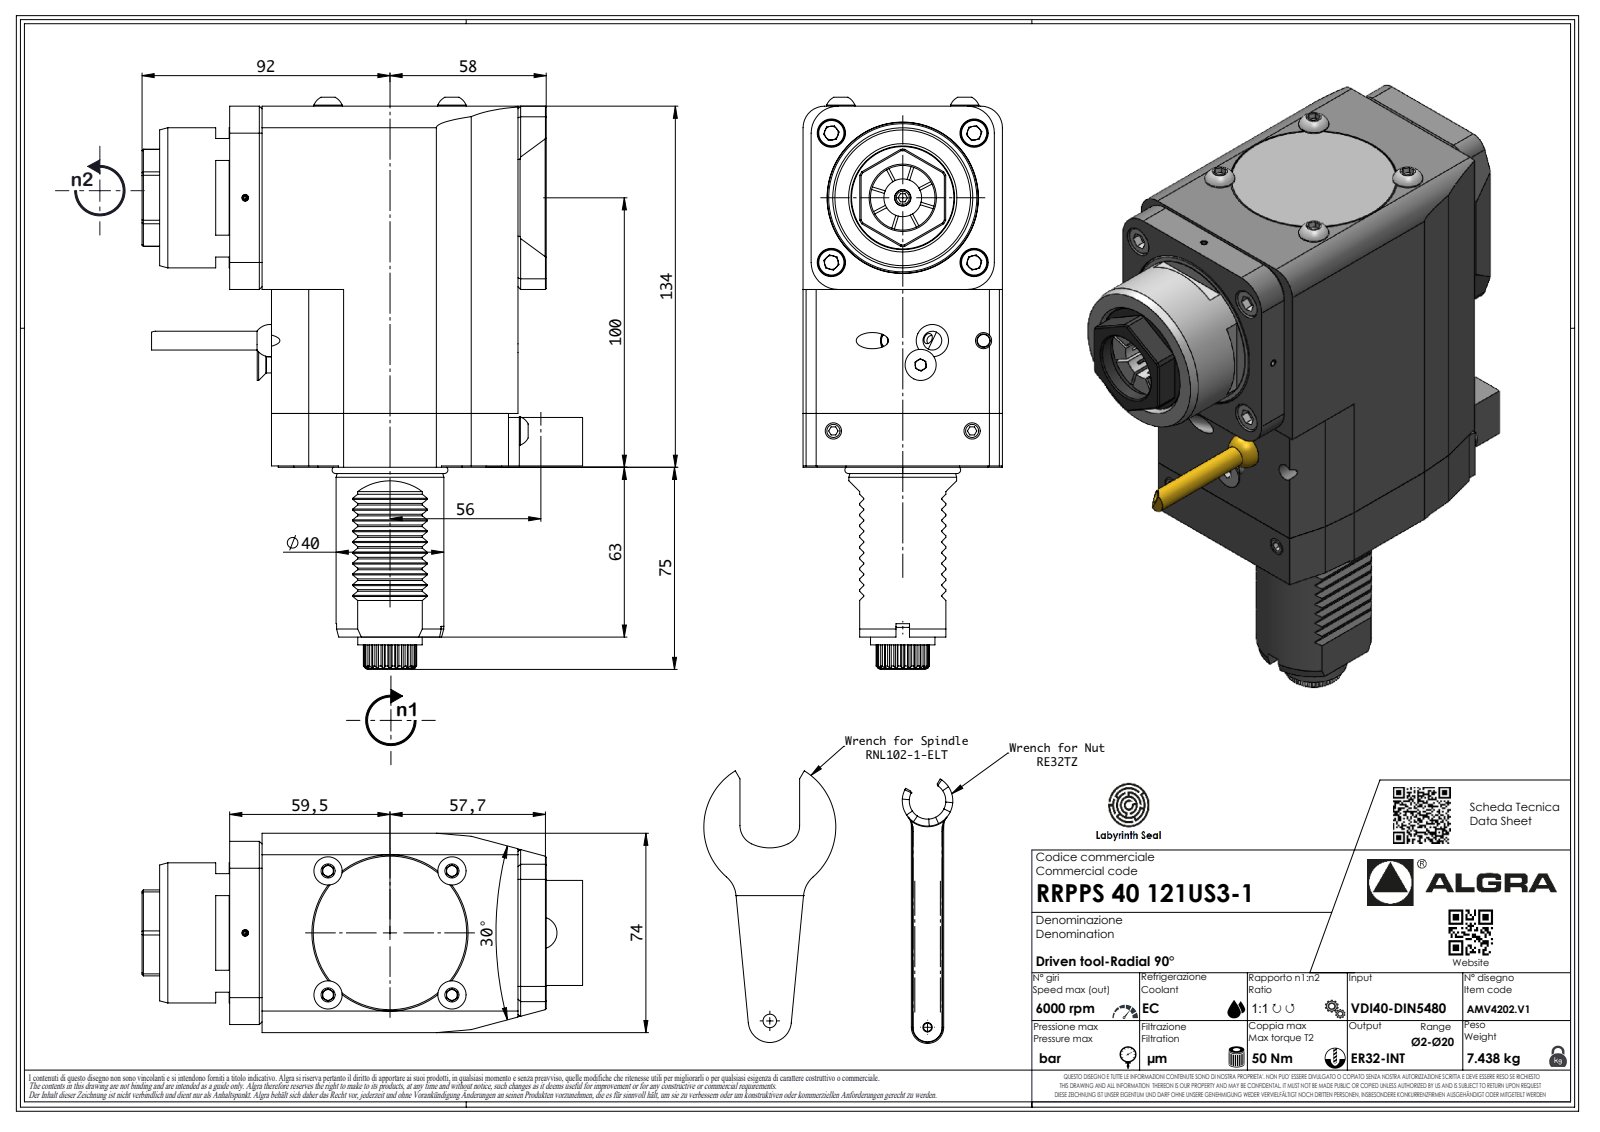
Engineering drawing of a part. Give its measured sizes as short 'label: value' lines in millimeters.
name: RRPPS40121US3-1
written by: SolidWorks 2023 (AUTOMOTIVE_DESIGN)
unit: mm
bodies: 6 solids, 725 faces (476 planar, 109 cylindrical, 140 other)
size: 209 × 163.55 × 74
volume: 1 202 000 mm³; area: 98 445 mm²
holes: 1× ⌀4, 1× ⌀4.2, 1× ⌀5
bosses: 2× ⌀40, 1× ⌀52, 1× ⌀38.7, 1× ⌀23.9, 1× ⌀12.73, 1× ⌀11.57, 1× ⌀7, 1× ⌀6
rounds: 20× R0.3, 7× R0.67, 7× R1.04, 7× R7.41, 4× R6, 4× R10, 2× R8, 1× R0.42
face distances: 10.5, 74, 91.5, 102, 134, 3.5, 0.5, 133.5, 103.5, 15.5
